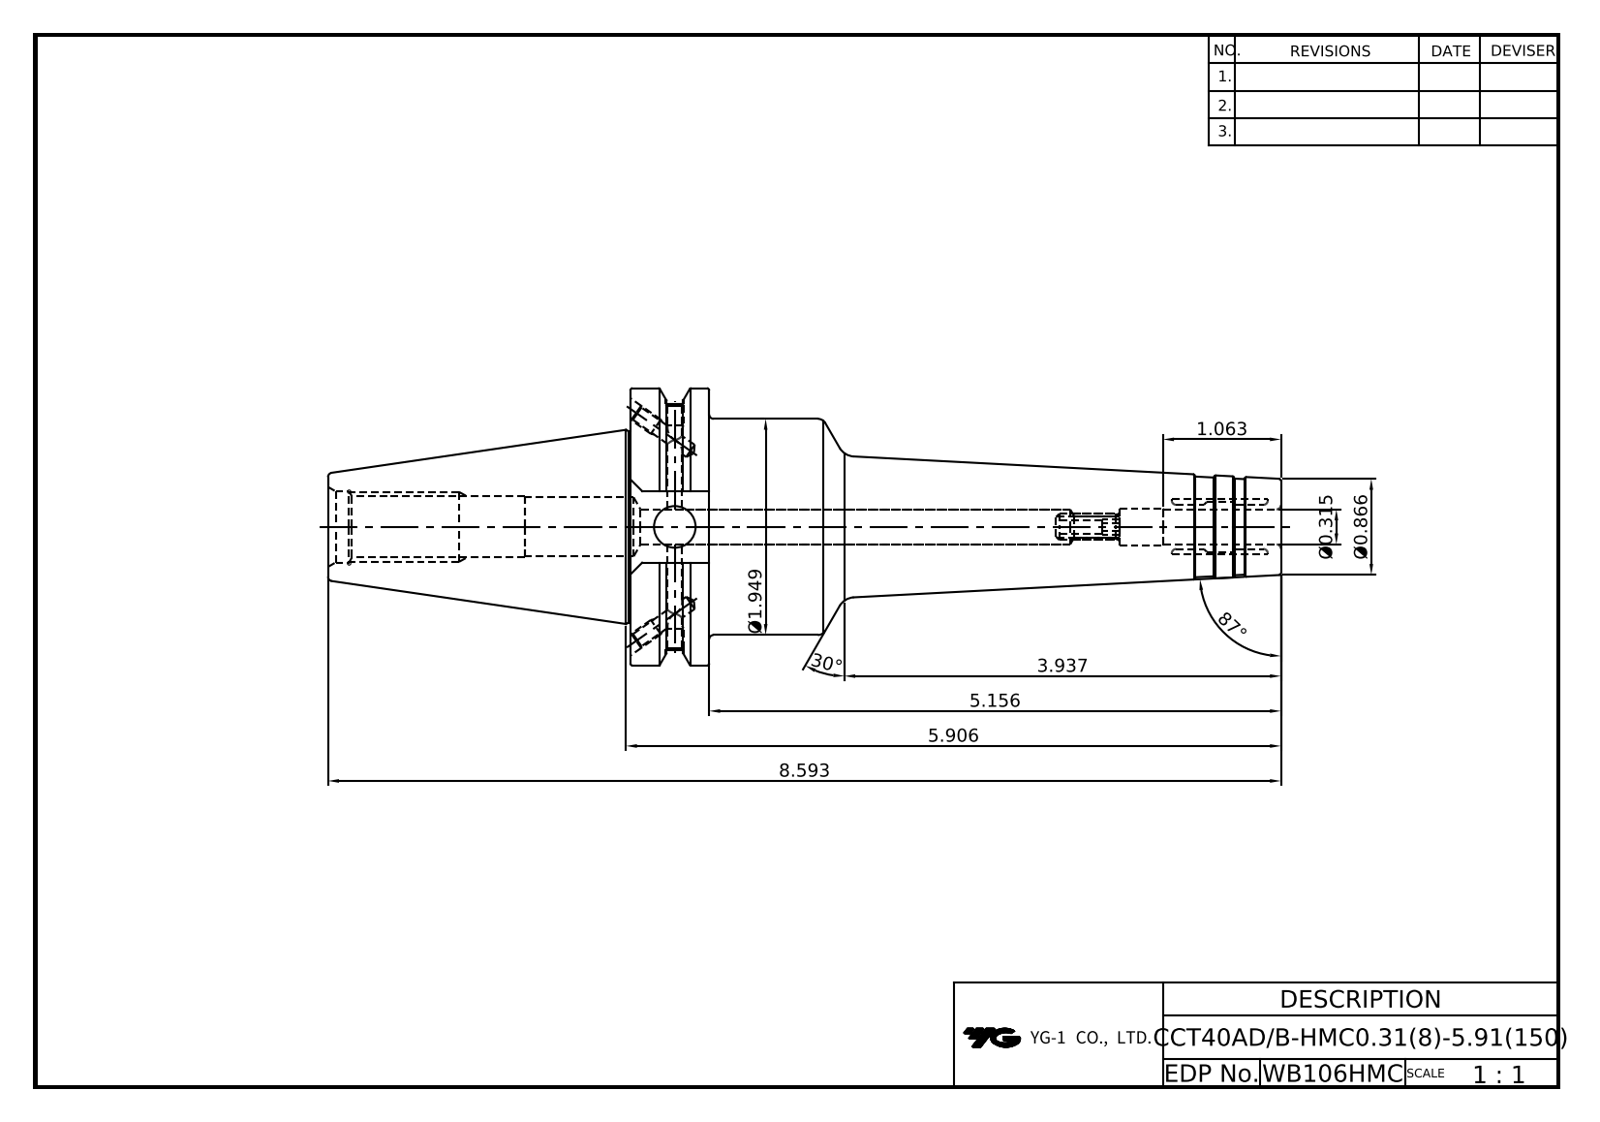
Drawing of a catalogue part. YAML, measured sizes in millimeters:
part_name: "LO-CCT40ADB-HMC8-150"
step_written_by: "Autodesk Inventor 2020 (AUTOMOTIVE_DESIGN)"
units: millimeters
bodies: {solids: 1, faces: 108, planar: 35, cylindrical: 31, other: 42}
overall_size: [218.25, 63.5, 61.09]
volume: 214120
surface_area: 36395
round_holes:
  - {diameter: 3.24, count: 4}
  - {diameter: 4, count: 2}
  - {diameter: 4.2, count: 2}
  - {diameter: 4.92, count: 1}
  - {diameter: 8, count: 1}
  - {diameter: 8.6, count: 1}
  - {diameter: 9.53, count: 1}
  - {diameter: 13, count: 1}
  - {diameter: 13.39, count: 1}
  - {diameter: 16.3, count: 1}
round_bosses_or_shafts:
  - {diameter: 63.5, count: 1}
  - {diameter: 49.5, count: 1}
  - {diameter: 43.8, count: 1}
partial_cylinders:
  - {radius: 8.19, count: 1}
  - {radius: 28.15, count: 1}
face_to_face_distances: [18.05, 149, 130.95, 47.6, 16.38, 69.25, 87.3, 218.25, 81.34, 12.09]
